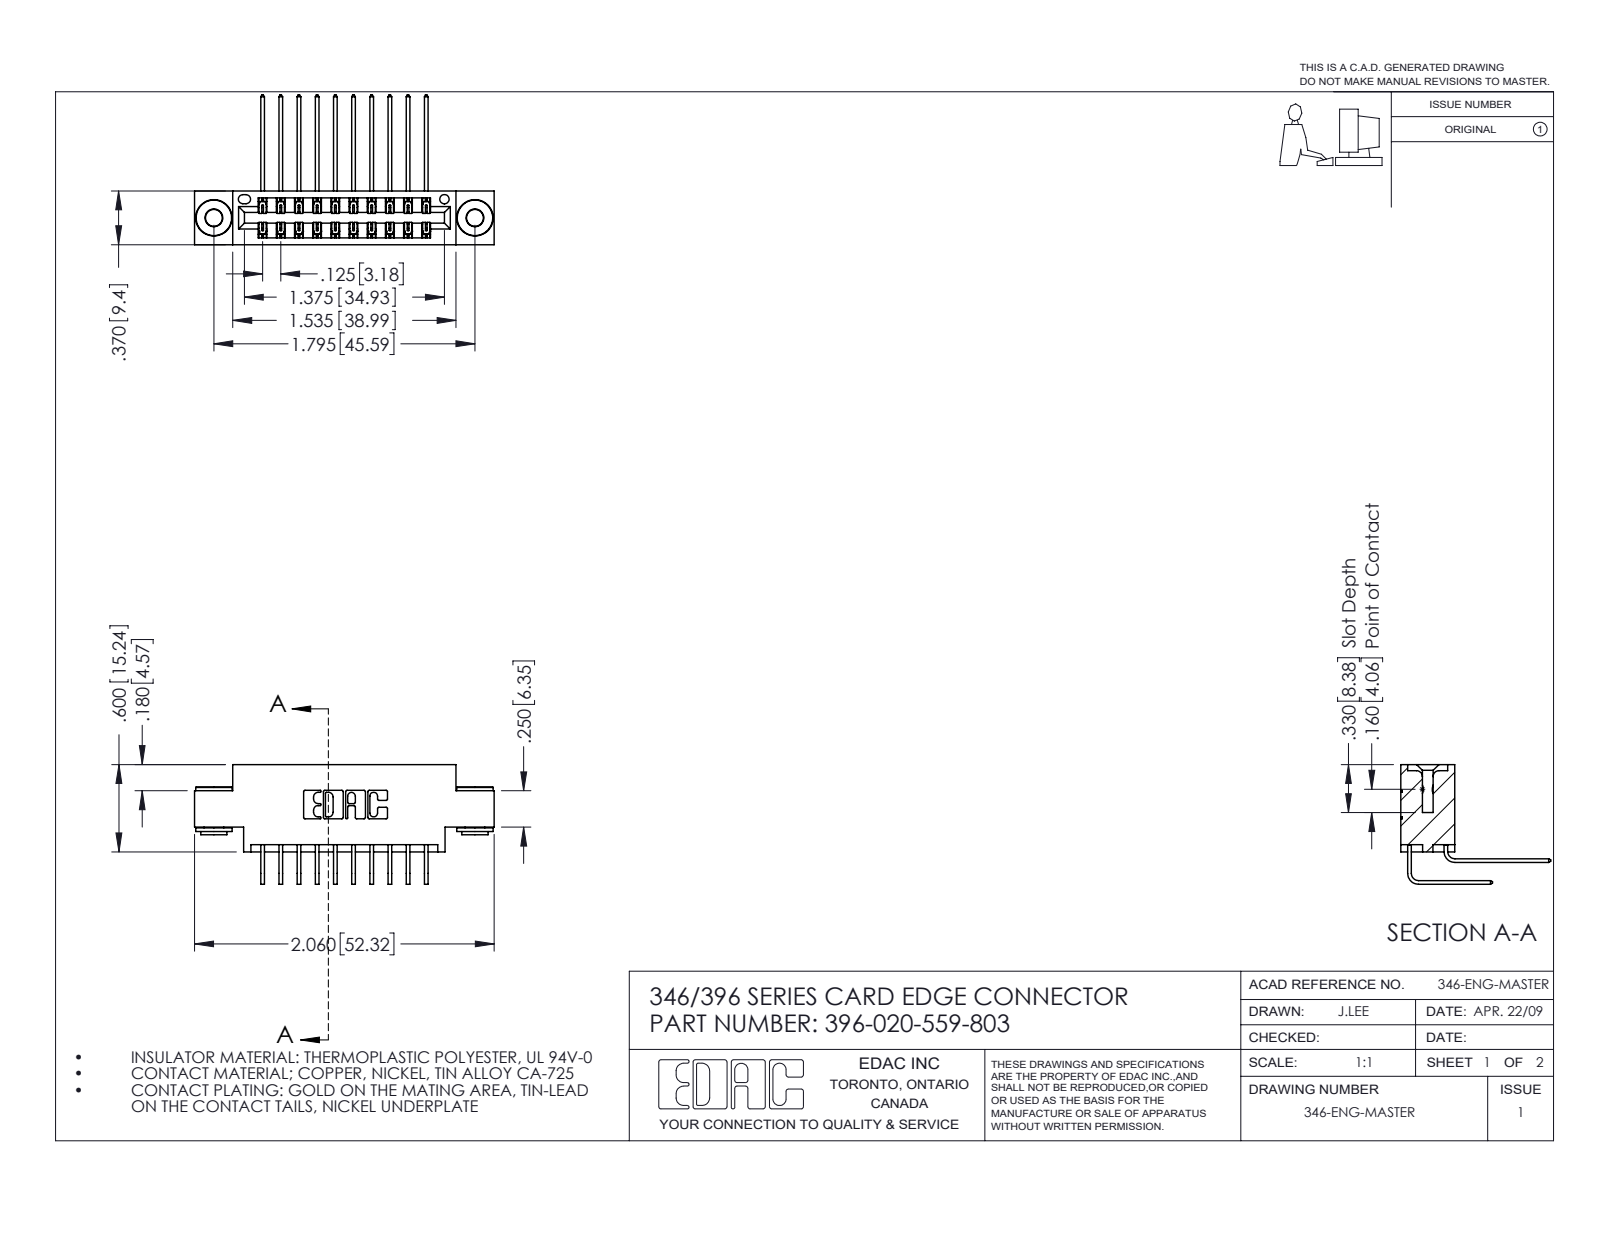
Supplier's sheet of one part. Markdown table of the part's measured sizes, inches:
| quantity | value |
| --- | --- |
| part name | 345-250-002_345-250-002-102; 345-292-001_558 559 Tail - 1; 345-292-001_559 Tail - 2; 346 Part_0.170 Offset - 0.156 Dia-TH (+1 more) |
| STEP written by | SolidWorks 2016 (CONFIG_CONTROL_DESIGN) |
| units | inches |
| bodies | 23 solids, 1244 faces (830 planar, 406 cylindrical, 8 other) |
| overall size | 2.06 × 1.03 × 0.823 |
| volume | 0.295 in³ |
| surface area | 10.99 in² |
| round holes (diameter × count) | 0.116 × 2, 0.156 × 2, 0.064 × 1 |
| round bosses / shafts (diameter × count) | 0.25 × 2, 0.18 × 2, 0.136 × 2 |
| partial cylindrical surfaces (radius × count) | 0.006 × 30, 0.01 × 22, 0.007 × 6, 0.031 × 6, 0.026 × 3, 0.014 × 2, 0.022 × 2, 0.024 × 2 |
| main face-to-face distances | 0.25, 0.048, 0.37, 0.322, 0.025, 0.072, 0.275, 0.298, 0.148, 0.222 |
| hole center spacings | 0.246, 1.59, 1.795 |
